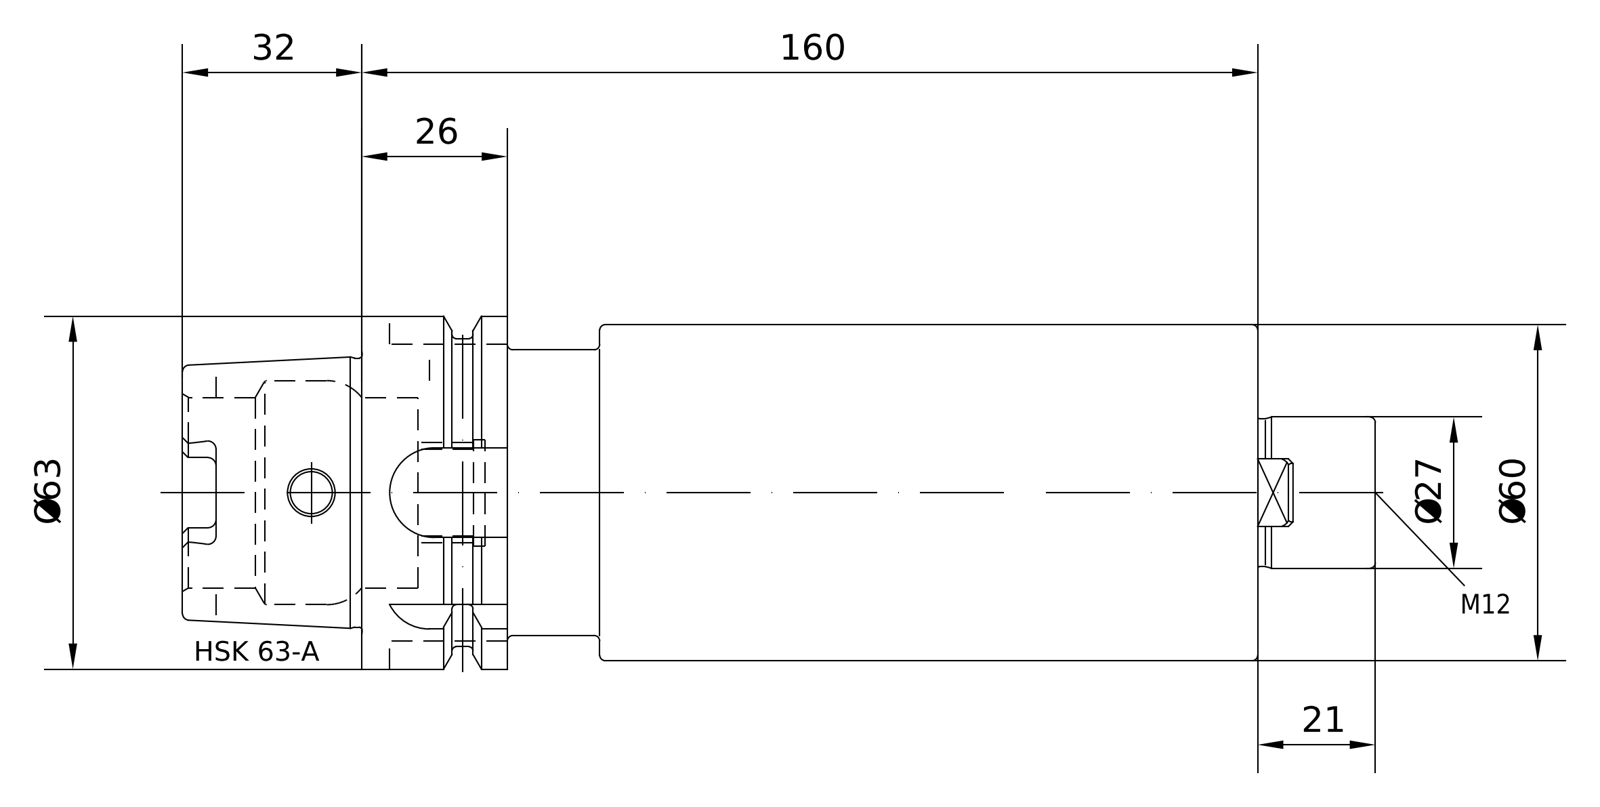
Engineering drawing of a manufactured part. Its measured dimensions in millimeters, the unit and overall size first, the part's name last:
Units: millimetres
Overall size (bounding box): 213 × 63 × 63
Round holes (diameter × count): ⌀7.5 ×1, ⌀10 ×1, ⌀10.2 ×1, ⌀12 ×1, ⌀16.92 ×1, ⌀18.32 ×1, ⌀18.66 ×1, ⌀34 ×1, ⌀40 ×1
Round bosses / shafts (diameter × count): ⌀63 ×1, ⌀60 ×1, ⌀55 ×1, ⌀51 ×1, ⌀48.04 ×1, ⌀27 ×1, ⌀18 ×1
Partial cylindrical surfaces — rounded edges, fillets, slot ends (radius × count): R1.5 ×6, R3 ×4, R8 ×1, R8.02 ×1, R9.02 ×1
Main face-to-face distances: 160, 26, 134, 10, 16, 150, 181, 155, 42, 42.5
Volume: 458 590 mm³ · Surface area: 53 099 mm²
Bodies: 1 solid, 198 faces (70 planar, 54 cylindrical, 74 other)
Part name (STEP PRODUCT): A63-052-27
STEP written by: PRO/ENGINEER BY PARAMETRIC TECHNOLOGY CORPORATION, 2010430 (CONFIG_CONTROL_DESIGN)
